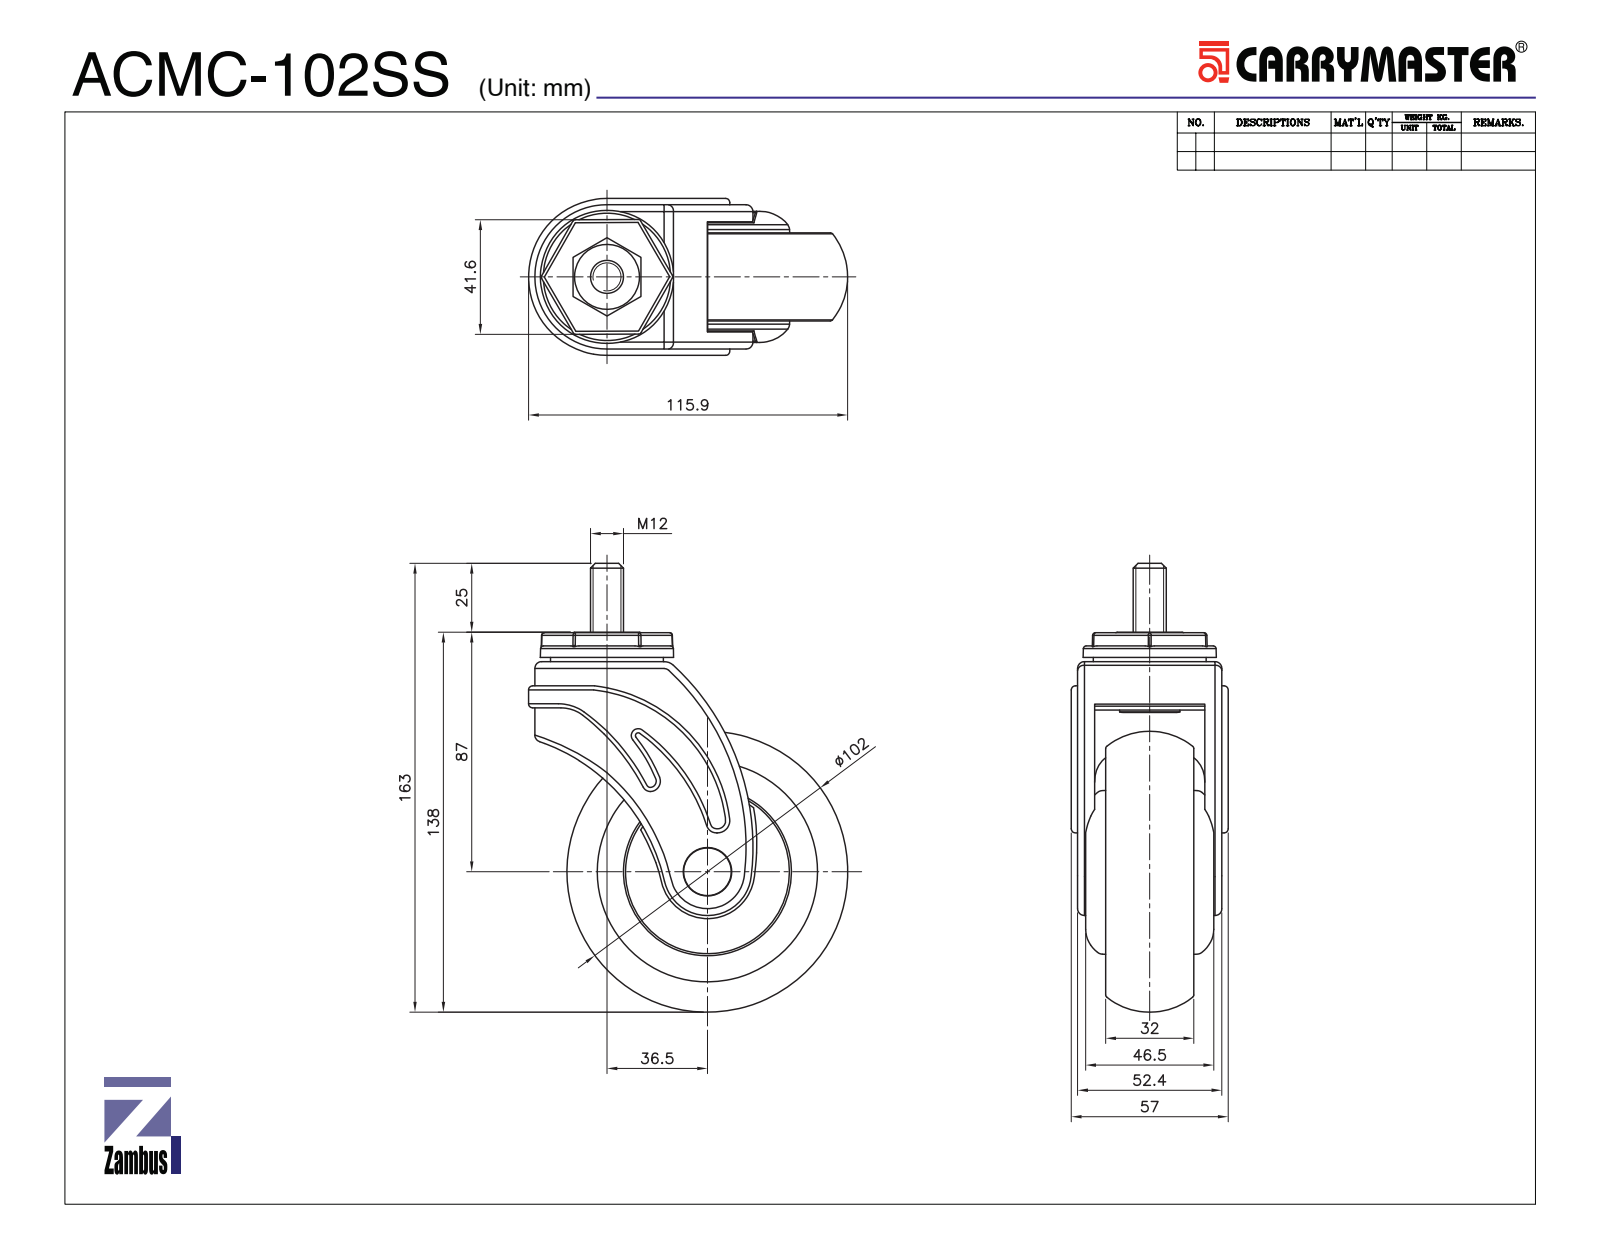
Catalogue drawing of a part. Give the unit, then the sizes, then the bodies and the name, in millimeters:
Units: millimetres
Overall size (bounding box): 162.9 × 115.7 × 56.4
Round holes (diameter × count): ⌀17.3 ×1, ⌀36 ×1, ⌀40.4 ×1, ⌀61 ×1, ⌀80.01 ×1
Round bosses / shafts (diameter × count): ⌀80 ×1, ⌀60 ×1, ⌀59.5 ×1, ⌀41 ×1, ⌀24 ×1, ⌀22 ×1, ⌀17 ×1, ⌀10.25 ×1
Partial cylindrical surfaces — rounded edges, fillets, slot ends (radius × count): R1 ×13, R1.5 ×2, R2.5 ×2, R3.8 ×2, R3 ×1, R4.5 ×1, R5 ×1, R13 ×1
Main face-to-face distances: 4.2, 36.2, 6, 10.2, 42.2, 46.4, 32, 40.4, 6.25, 46.15
Volume: 371 893 mm³ · Surface area: 65 159 mm²
Bodies: 4 solids, 282 faces (67 planar, 125 cylindrical, 90 other)
Part name (STEP PRODUCT): ACMC-102 WHEEL; ACMC-102 NON BRAKE FRAME; 08. ACMC-102SS; ACMC-102 S TOP PLATE (+1 more)
STEP written by: SolidWorks 2019 (CONFIG_CONTROL_DESIGN)
